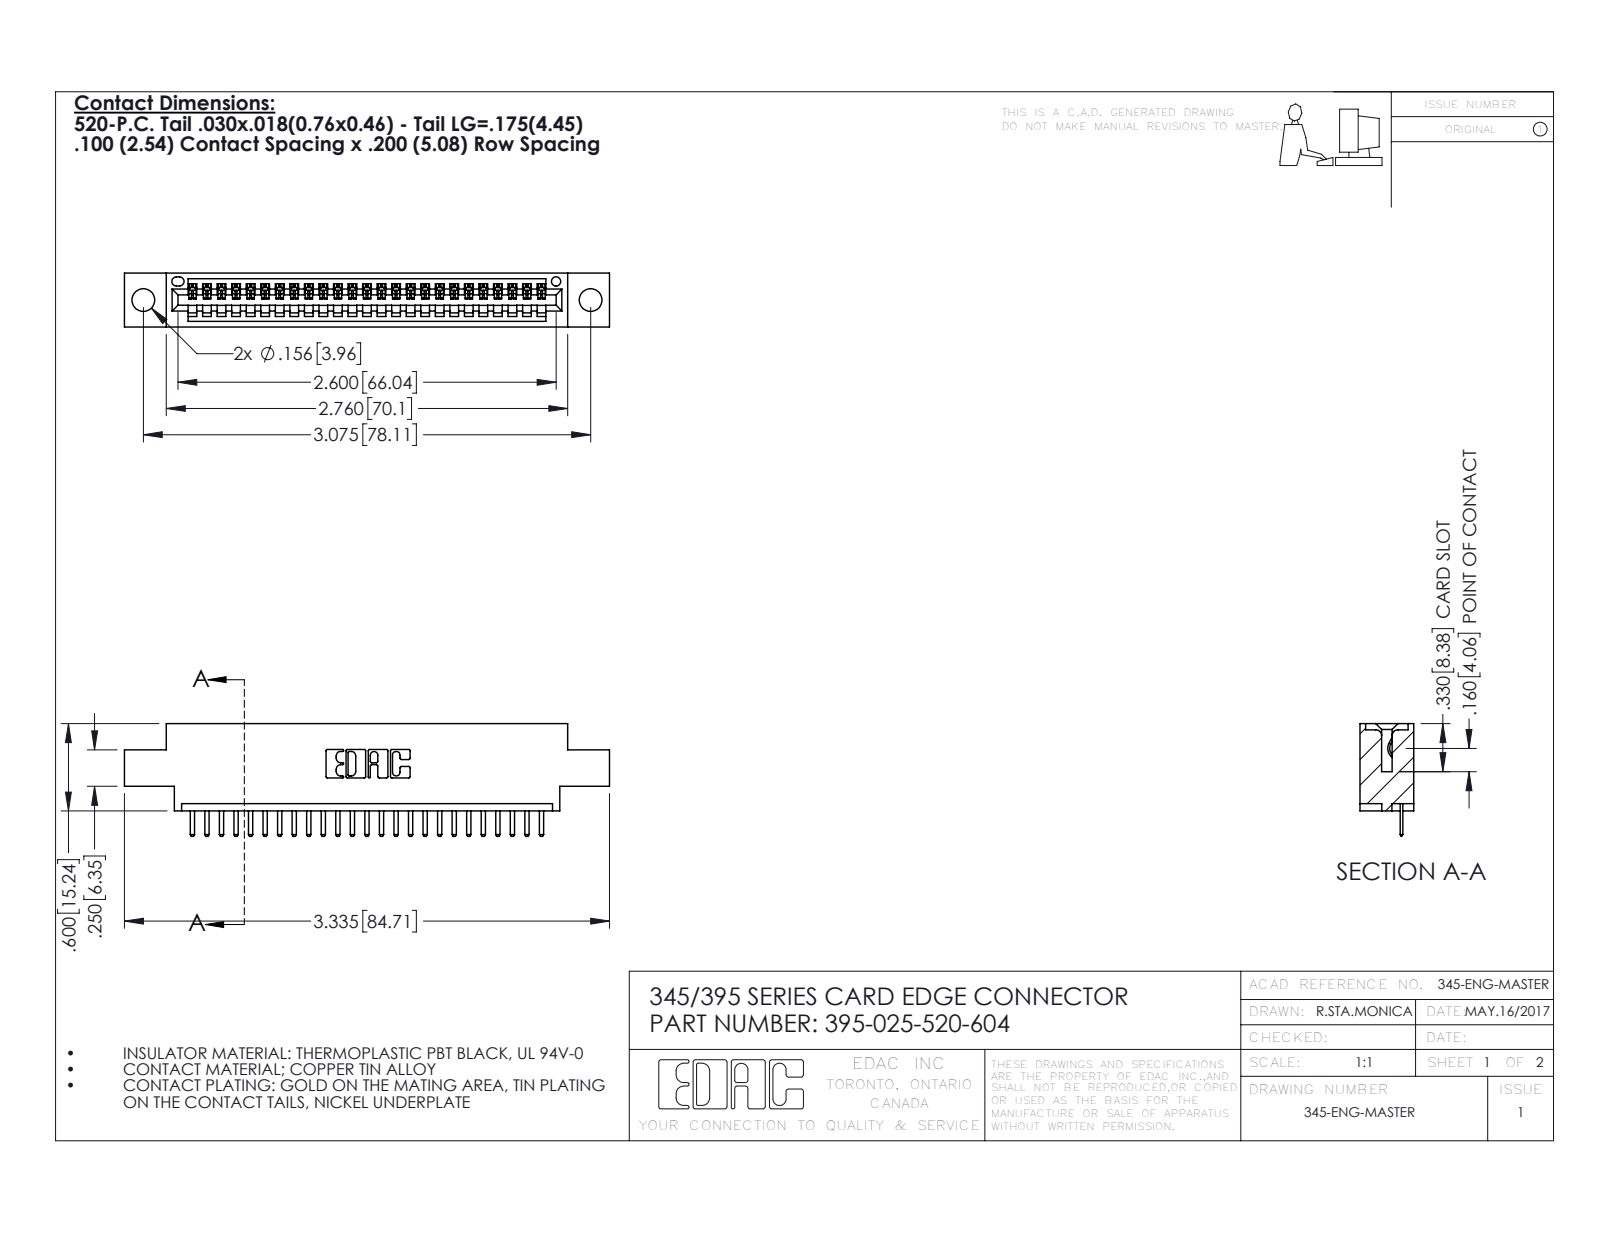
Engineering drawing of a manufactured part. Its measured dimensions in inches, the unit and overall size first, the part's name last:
Units: inches
Overall size (bounding box): 3.335 × 0.775 × 0.37
Round holes (diameter × count): ⌀0.156 ×2, ⌀0.064 ×1
Partial cylindrical surfaces — rounded edges, fillets, slot ends (radius × count): R0.01 ×52, R0.006 ×50, R0.01 ×22, R0.007 ×6, R0.031 ×6, R0.026 ×3, R0.031 ×2, R0.04 ×2
Main face-to-face distances: 0.298, 0.072, 0.37, 0.2, 0.098, 0.272, 0.025, 0.225, 0.072, 0.175
Hole centre spacings: 0.27, 2.84, 3.075
Volume: 0.466 in³ · Surface area: 14.9 in²
Bodies: 26 solids, 1680 faces (1134 planar, 546 cylindrical, 0 other)
Part name (STEP PRODUCT): 345 Part_0.170 Offset - 0.156 Dia-TH; 345-292-001_345-293-120; 395-025-520-604
STEP written by: SolidWorks 2016 (CONFIG_CONTROL_DESIGN)
